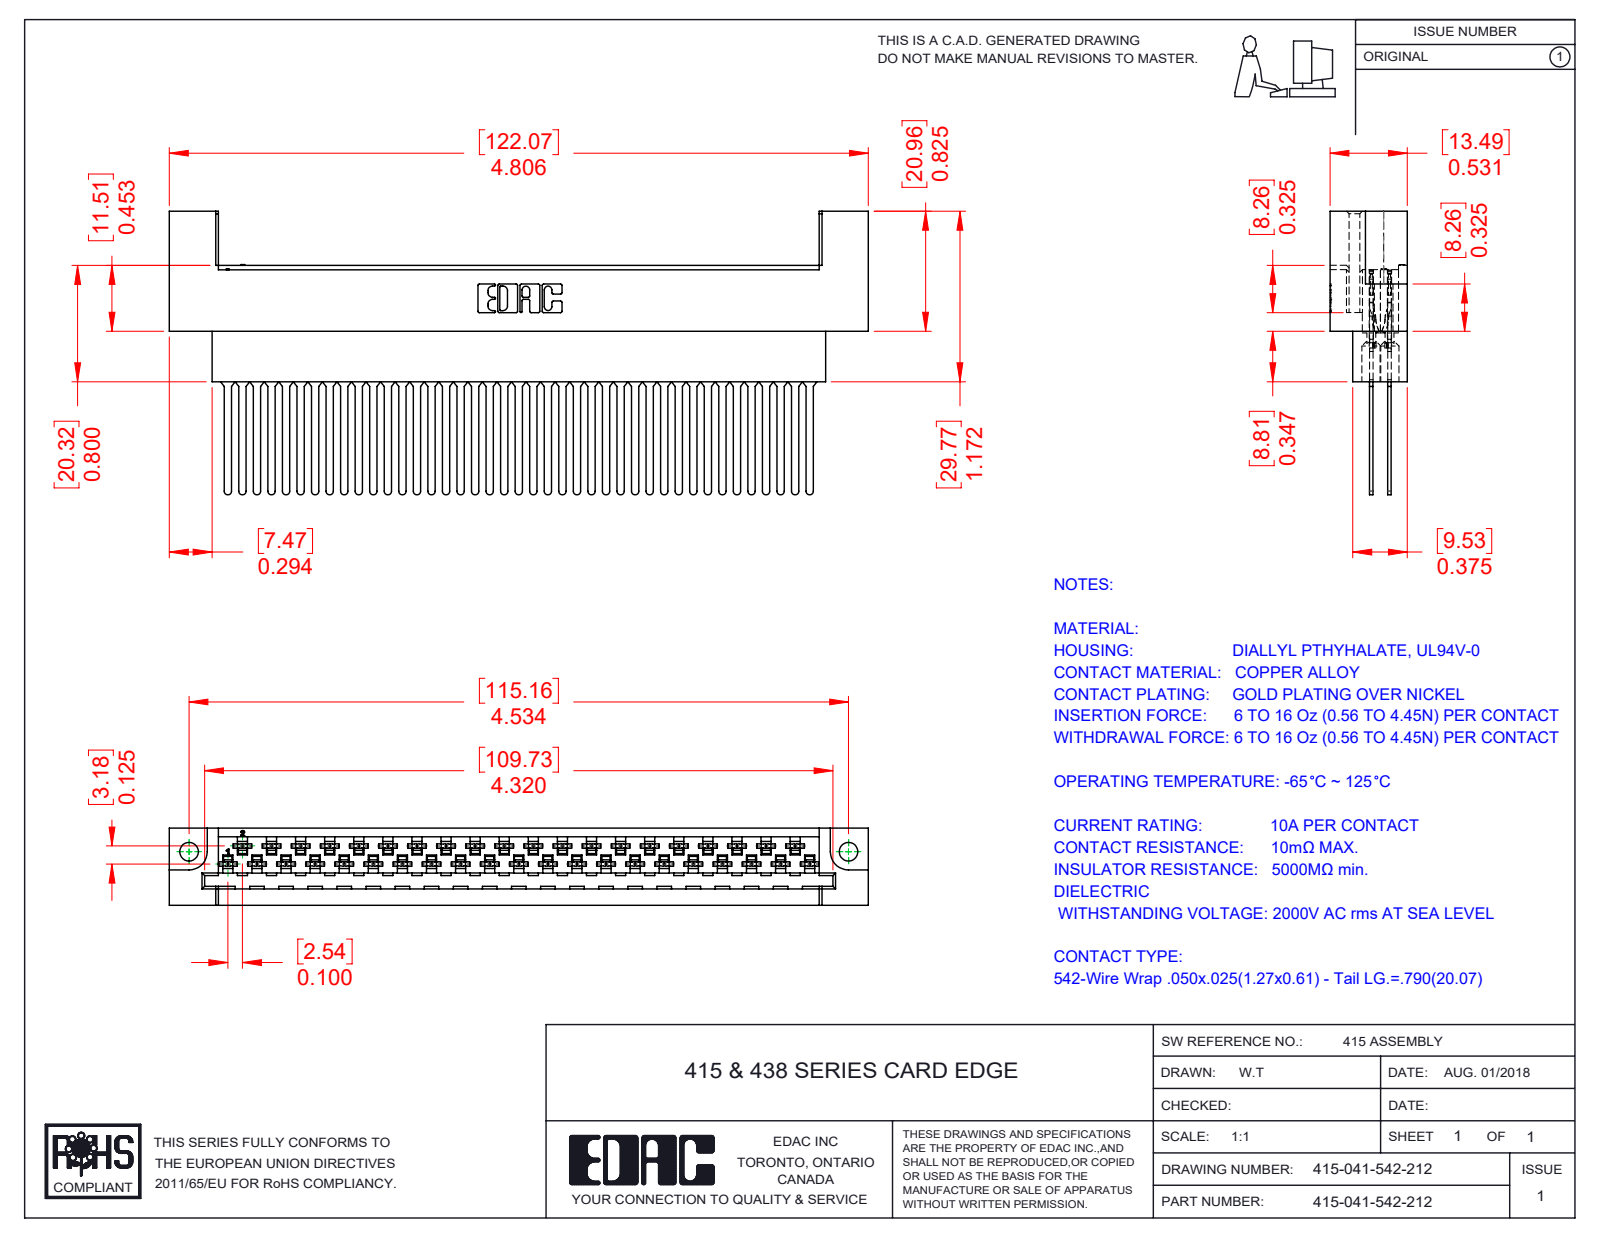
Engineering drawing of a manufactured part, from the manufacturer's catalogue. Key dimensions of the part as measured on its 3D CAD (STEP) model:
Part name (STEP PRODUCT): 516-290-001_542; 415-210-001_415-210-041-212; 415-041-542-212
STEP written by: SolidWorks 2016 (CONFIG_CONTROL_DESIGN)
Units: millimetres
Bodies: 42 solids, 4178 faces (2675 planar, 1112 cylindrical, 391 other)
Overall size (bounding box): 122.07 × 49.49 × 13.49
Volume: 22 088 mm³ · Surface area: 28 959 mm²
Round holes (diameter × count): ⌀1.27 ×41, ⌀3.3 ×41, ⌀3.25 ×2
Partial cylindrical surfaces — rounded edges, fillets, slot ends (radius × count): R0.3 ×164, R0.56 ×164, R0.18 ×82, R0.2 ×82, R0.41 ×82, R2.03 ×82, R0.64 ×41, R0.25 ×22
Main face-to-face distances: 3.18, 0.61, 1.88, 7.49, 13.49, 6.61, 6.88, 6, 1.27, 2.82
Hole centre spacings: 5.08, 10.16, 15.24, 20.32, 25.4, 30.48, 35.56, 2.54
